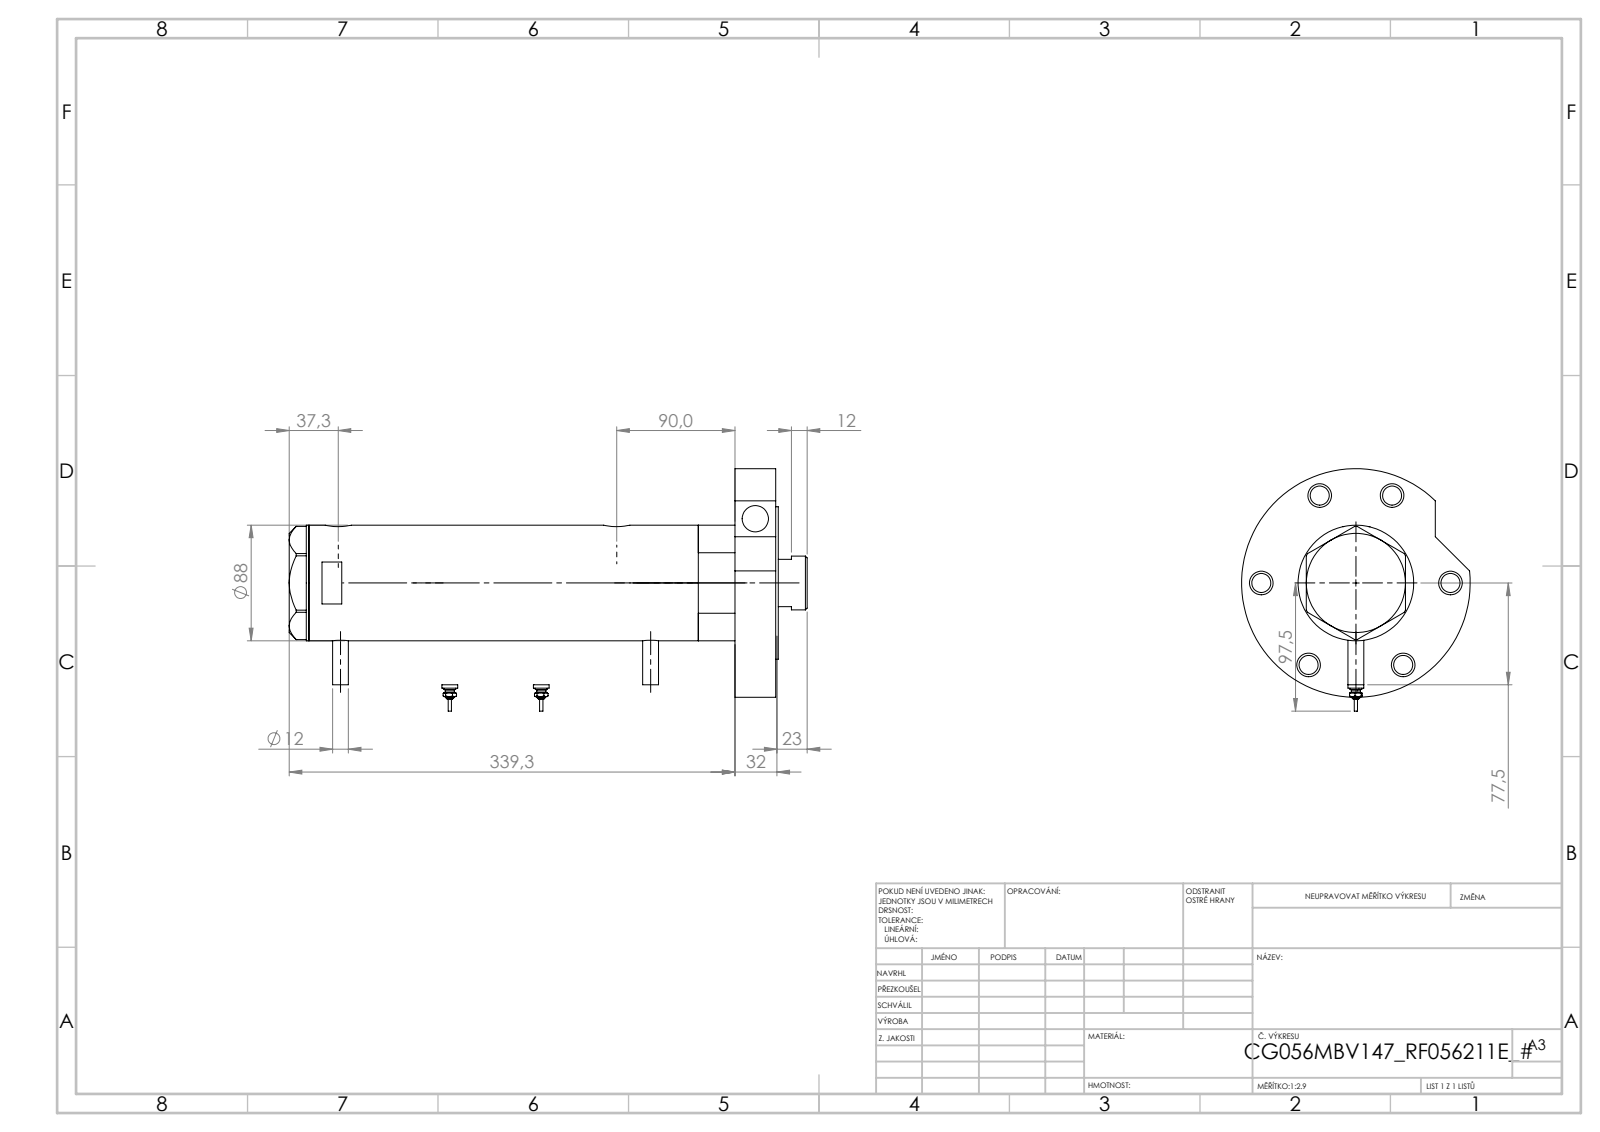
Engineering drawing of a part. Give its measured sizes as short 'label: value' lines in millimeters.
name: V270CG_RF211E; V270CG_MIDDLE; V270CG_FRONT; V270CG_BACK (+2 more)
written by: SolidWorks 2019 (CONFIG_CONTROL_DESIGN)
unit: mm
bodies: 7 solids, 257 faces (91 planar, 102 cylindrical, 64 other)
size: 394.3 × 184.5 × 174
volume: 2 564 000 mm³; area: 360 823 mm²
holes: 7× ⌀14.5, 6× ⌀18, 3× ⌀20, 2× ⌀12.5, 2× ⌀13.16, 1× ⌀42, 1× ⌀43.5, 1× ⌀56, 1× ⌀60, 1× ⌀75, 1× ⌀80
bosses: 4× ⌀12, 2× ⌀9, 2× ⌀7, 2× ⌀4.5, 2× ⌀2.5, 1× ⌀174, 1× ⌀116, 1× ⌀88
face distances: 31, 2, 357.3, 324.3, 355.3, 33, 234.4, 89.9, 120.9, 122.9
hole spacings: 72, 80, 119.73, 124.71, 129.15, 143.69, 1.7, 25.8
